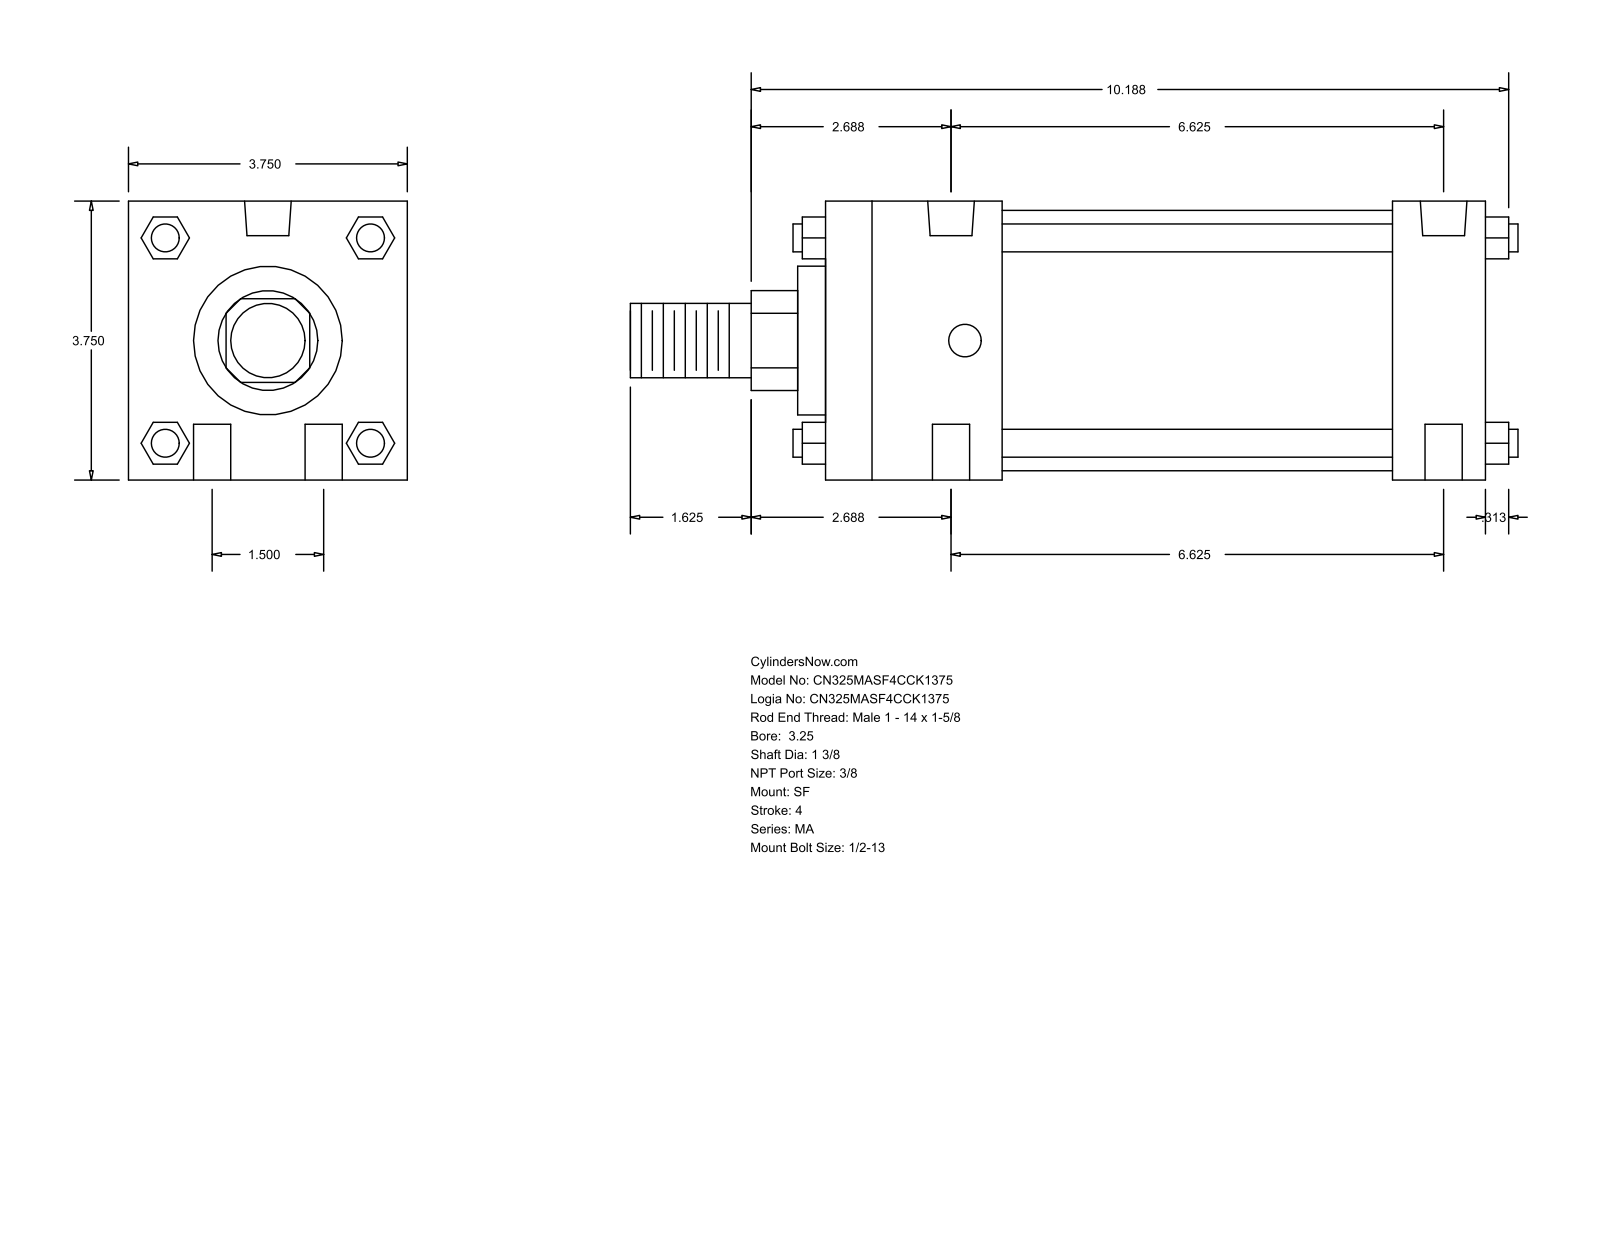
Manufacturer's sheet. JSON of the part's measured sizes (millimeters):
{"part_name": "MA_SF__0325_1.375", "step_written_by": "GSSL Pune (CONFIG_CONTROL_DESIGN)", "units": "millimeters", "bodies": {"solids": 0, "faces": 124, "planar": 94, "cylindrical": 30, "other": 0}, "overall_size": [303.21, 95.25, 95.25], "round_holes": [[12.7, 4], [11.11, 2], [15.93, 2]], "round_bosses_or_shafts": [[9.53, 4], [88.9, 1], [50.8, 1], [34.92, 1], [25.4, 1]], "partial_cylinders_radius": [[17.06, 1]], "face_to_face_distances": [95.24, 225.42, 193.67, 31.75, 60.32, 133.35, 165.1, 9.52, 69.84, 203.19], "hole_center_spacings": [19.05, 169.35, 168.28, 38.1, 172.54, 158.75]}
